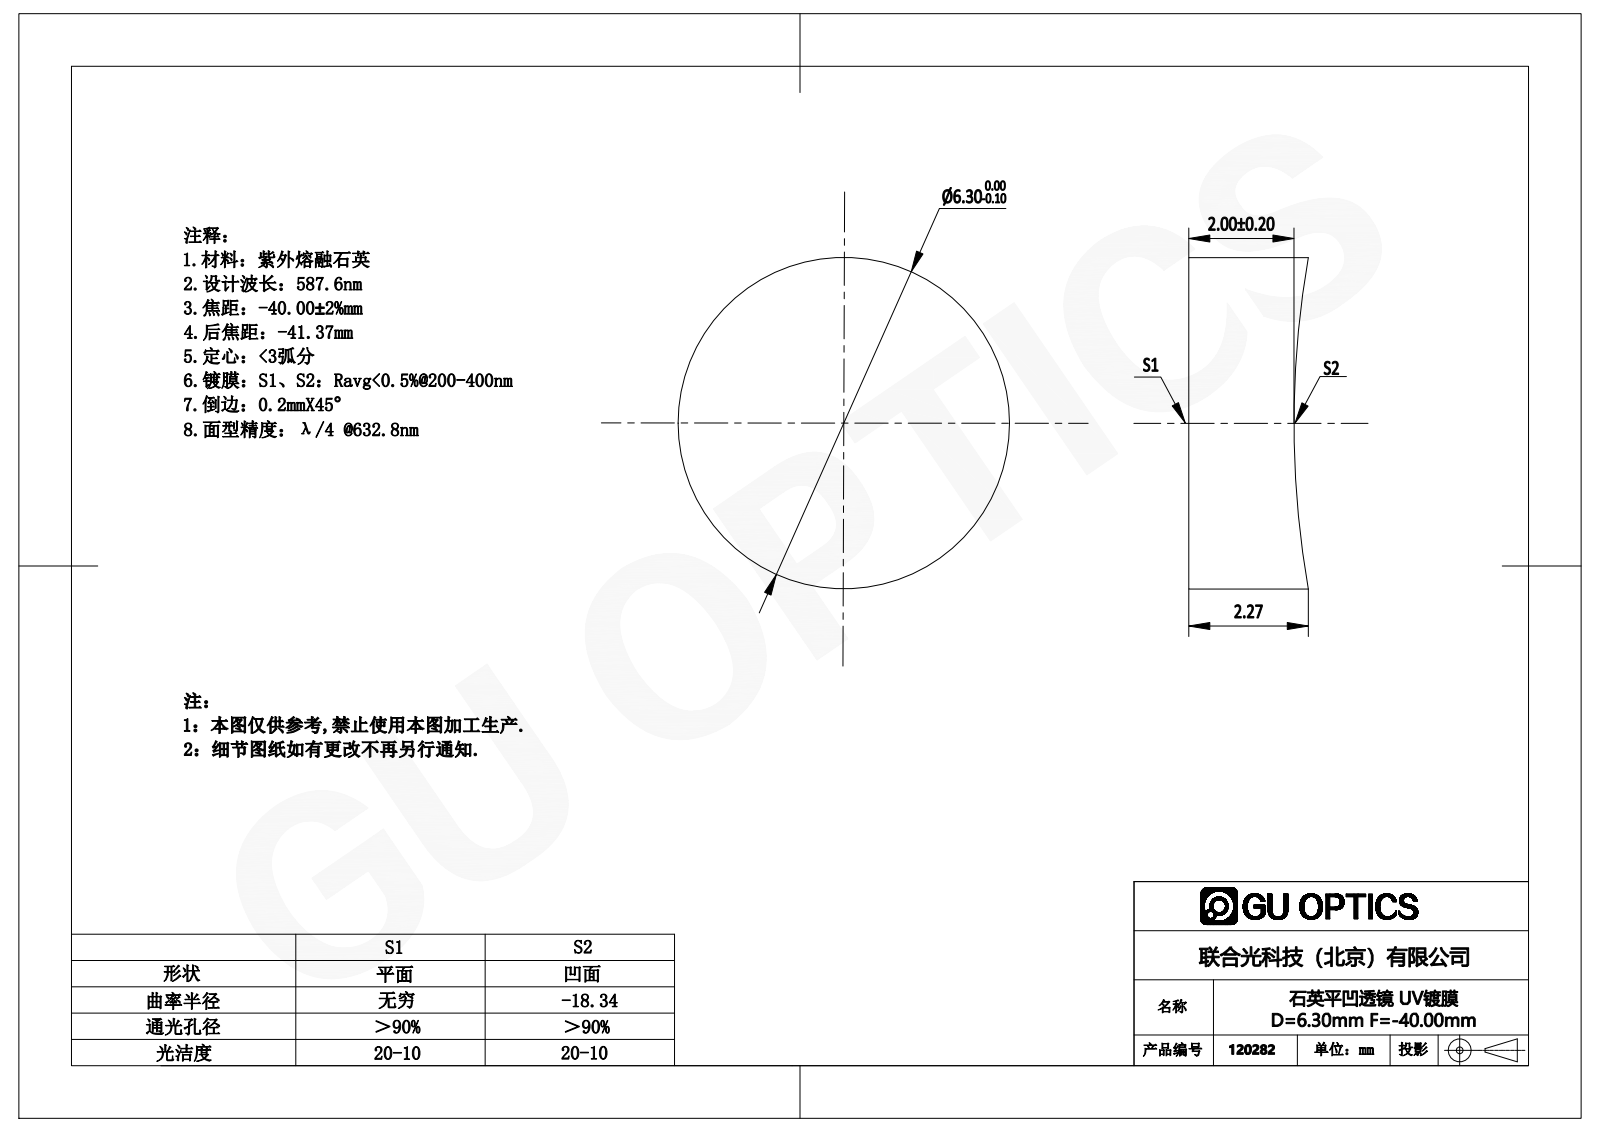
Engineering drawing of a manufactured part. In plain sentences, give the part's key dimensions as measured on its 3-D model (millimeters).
The part is named "120249". Its 3-D file was written by "SolidWorks 2016 (AUTOMOTIVE_DESIGN)". It is 1 solid with 5 faces: 1 planar, 2 cylindrical and 2 other. Overall it measures 6.3 by 6.3 by 2.27 millimeters. Its volume is 67 cubic millimeters and its surface area 108 square millimeters. Round bosses or shafts: 1 of diameter 6.3.
